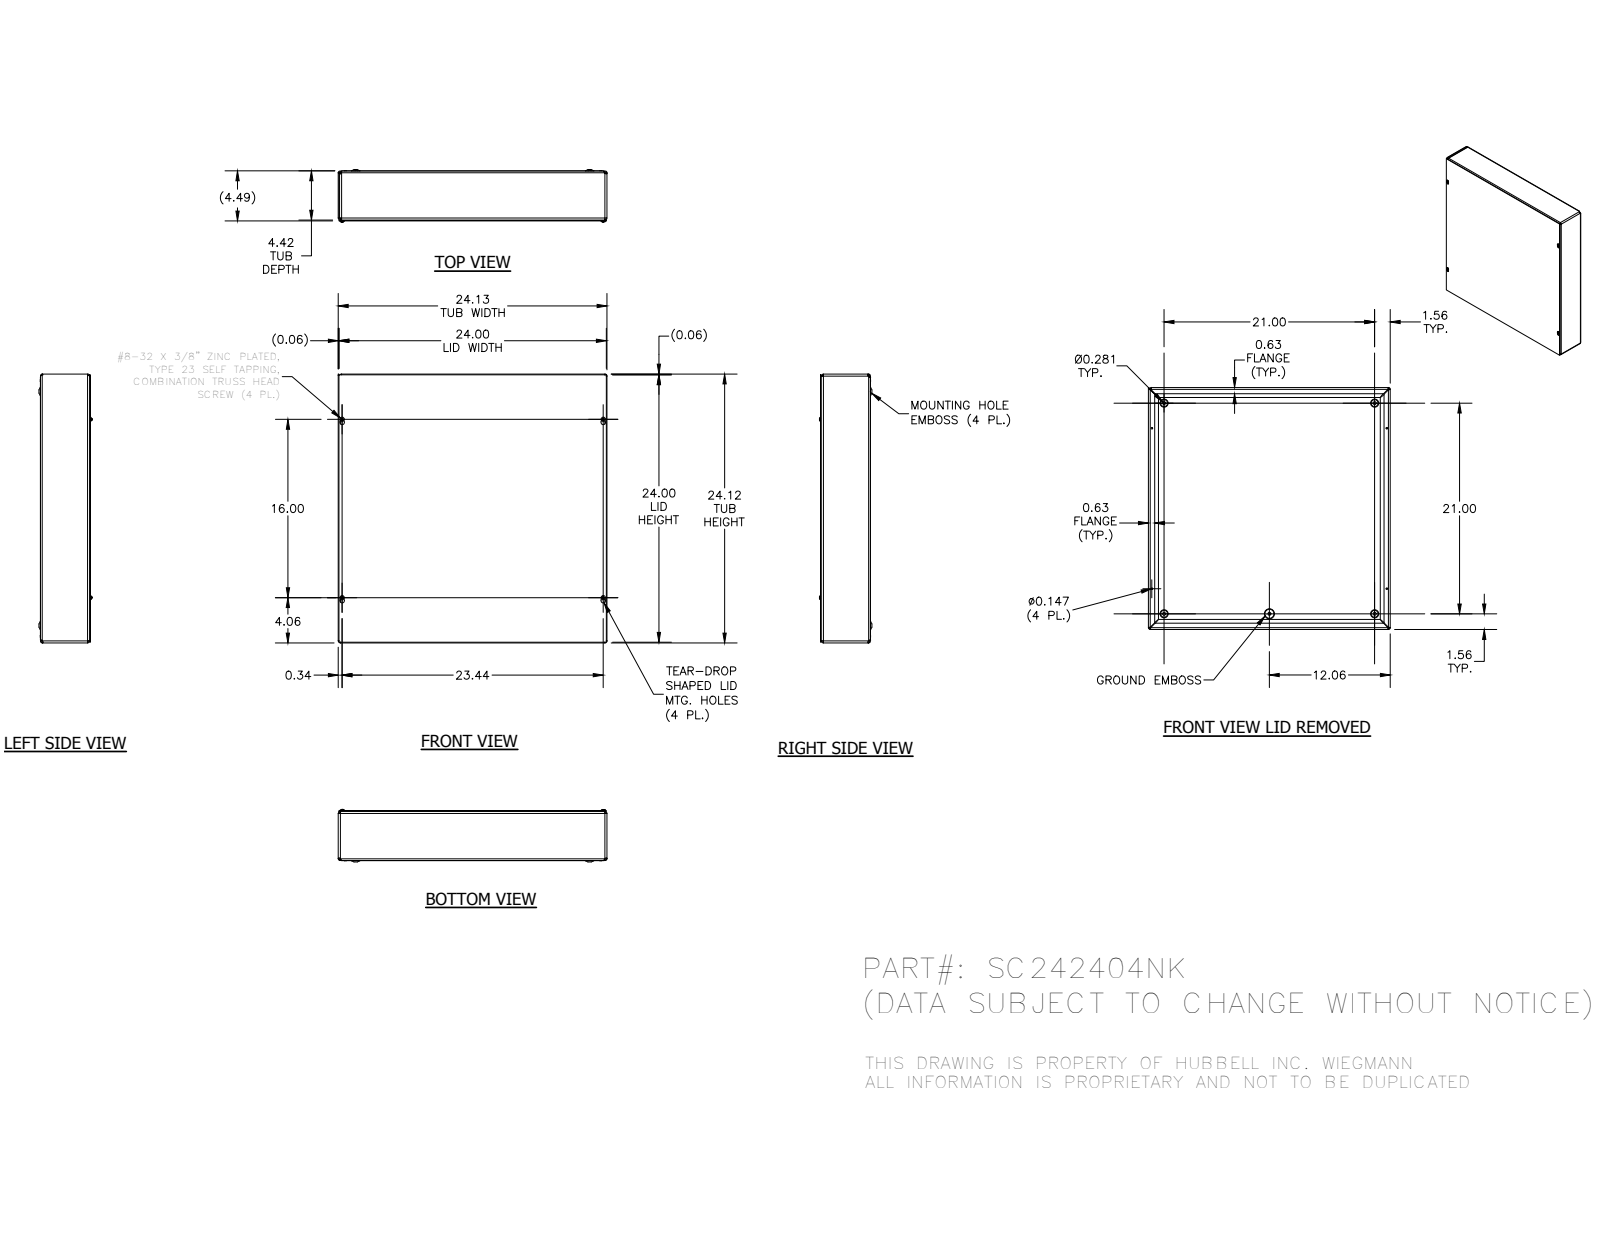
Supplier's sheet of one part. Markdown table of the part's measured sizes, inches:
| quantity | value |
| --- | --- |
| part name | SC2424BKP; SC242404NKWRA; SC2424LID; 34056 (+1 more) |
| STEP written by | Autodesk Inventor 2014 (AUTOMOTIVE_DESIGN) |
| units | inches |
| bodies | 7 solids, 358 faces (133 planar, 75 cylindrical, 150 other) |
| overall size | 24.125 × 24.125 × 4.716 |
| volume | 118.3 in³ |
| surface area | 3 408 in² |
| round holes (diameter × count) | 0.147 × 4, 0.3 × 4, 0.165 × 1 |
| round bosses / shafts (diameter × count) | 0.18 × 8, 0.384 × 4, 0.164 × 4, 0.228 × 1 |
| partial cylindrical surfaces (radius × count) | 0.125 × 12, 0.187 × 8, 0.055 × 4, 0.062 × 4, 0.094 × 4, 0.117 × 4, 0.124 × 4, 0.156 × 4 |
| main face-to-face distances | 0.074, 4.417, 4.343, 4.491, 0.062, 24.063, 24.001, 0.062, 24.125, 24.125 |
| hole center spacings | 18.54, 21, 2.781, 2.781, 10.5, 16, 21.899, 22.359 |
